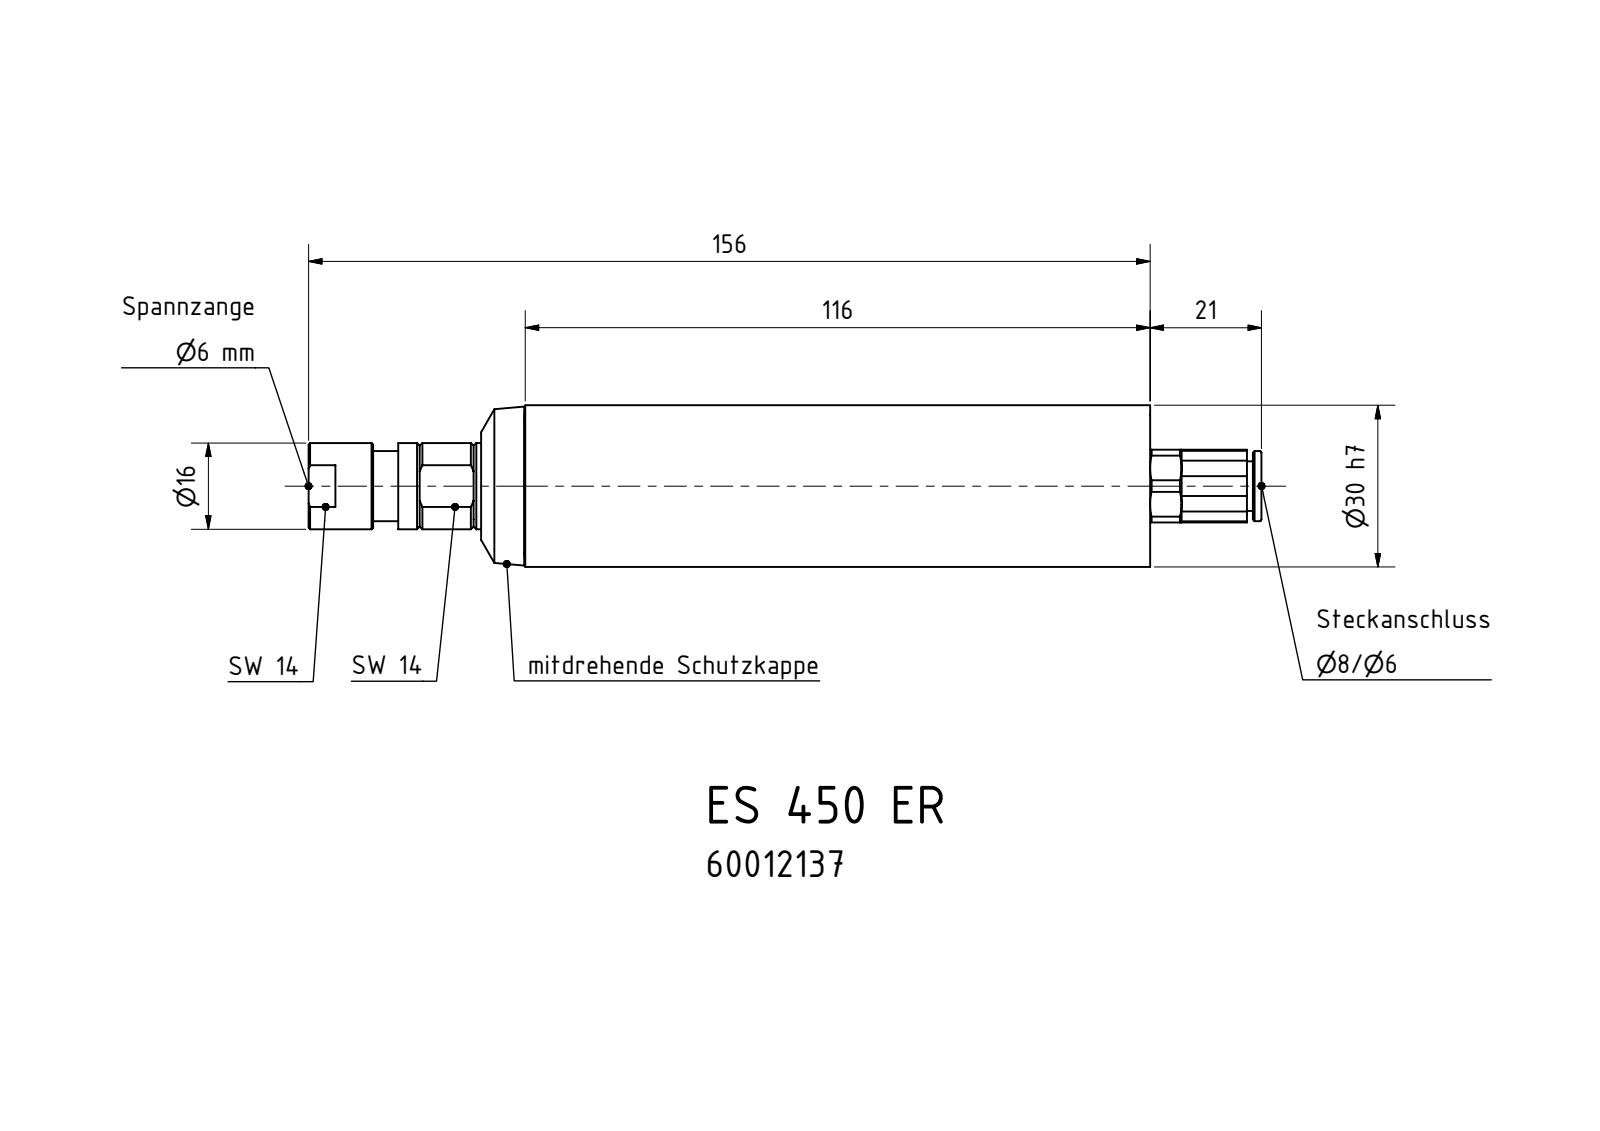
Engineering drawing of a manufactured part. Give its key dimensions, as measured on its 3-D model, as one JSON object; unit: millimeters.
{"part_name": "ES 450 ER_60012137", "step_written_by": "Autodesk Inventor 2008 (CONFIG_CONTROL_DESIGN)", "units": "millimeters", "bodies": {"solids": 1, "faces": 167, "planar": 84, "cylindrical": 41, "other": 42}, "overall_size": [176.94, 30, 30], "volume_mm3": 92989, "surface_area_mm2": 17483, "round_holes": [[6, 1], [8, 1], [9, 1]], "round_bosses_or_shafts": [[30, 1], [28.32, 1], [16, 1], [13, 1], [9.2, 1]], "partial_cylinders_radius": [[19, 8], [3.92, 1], [6.75, 1], [7.25, 1]], "face_to_face_distances": [13.5, 0.7, 13, 14, 156.24, 32.04, 124.2, 0.5, 18, 40.24]}
